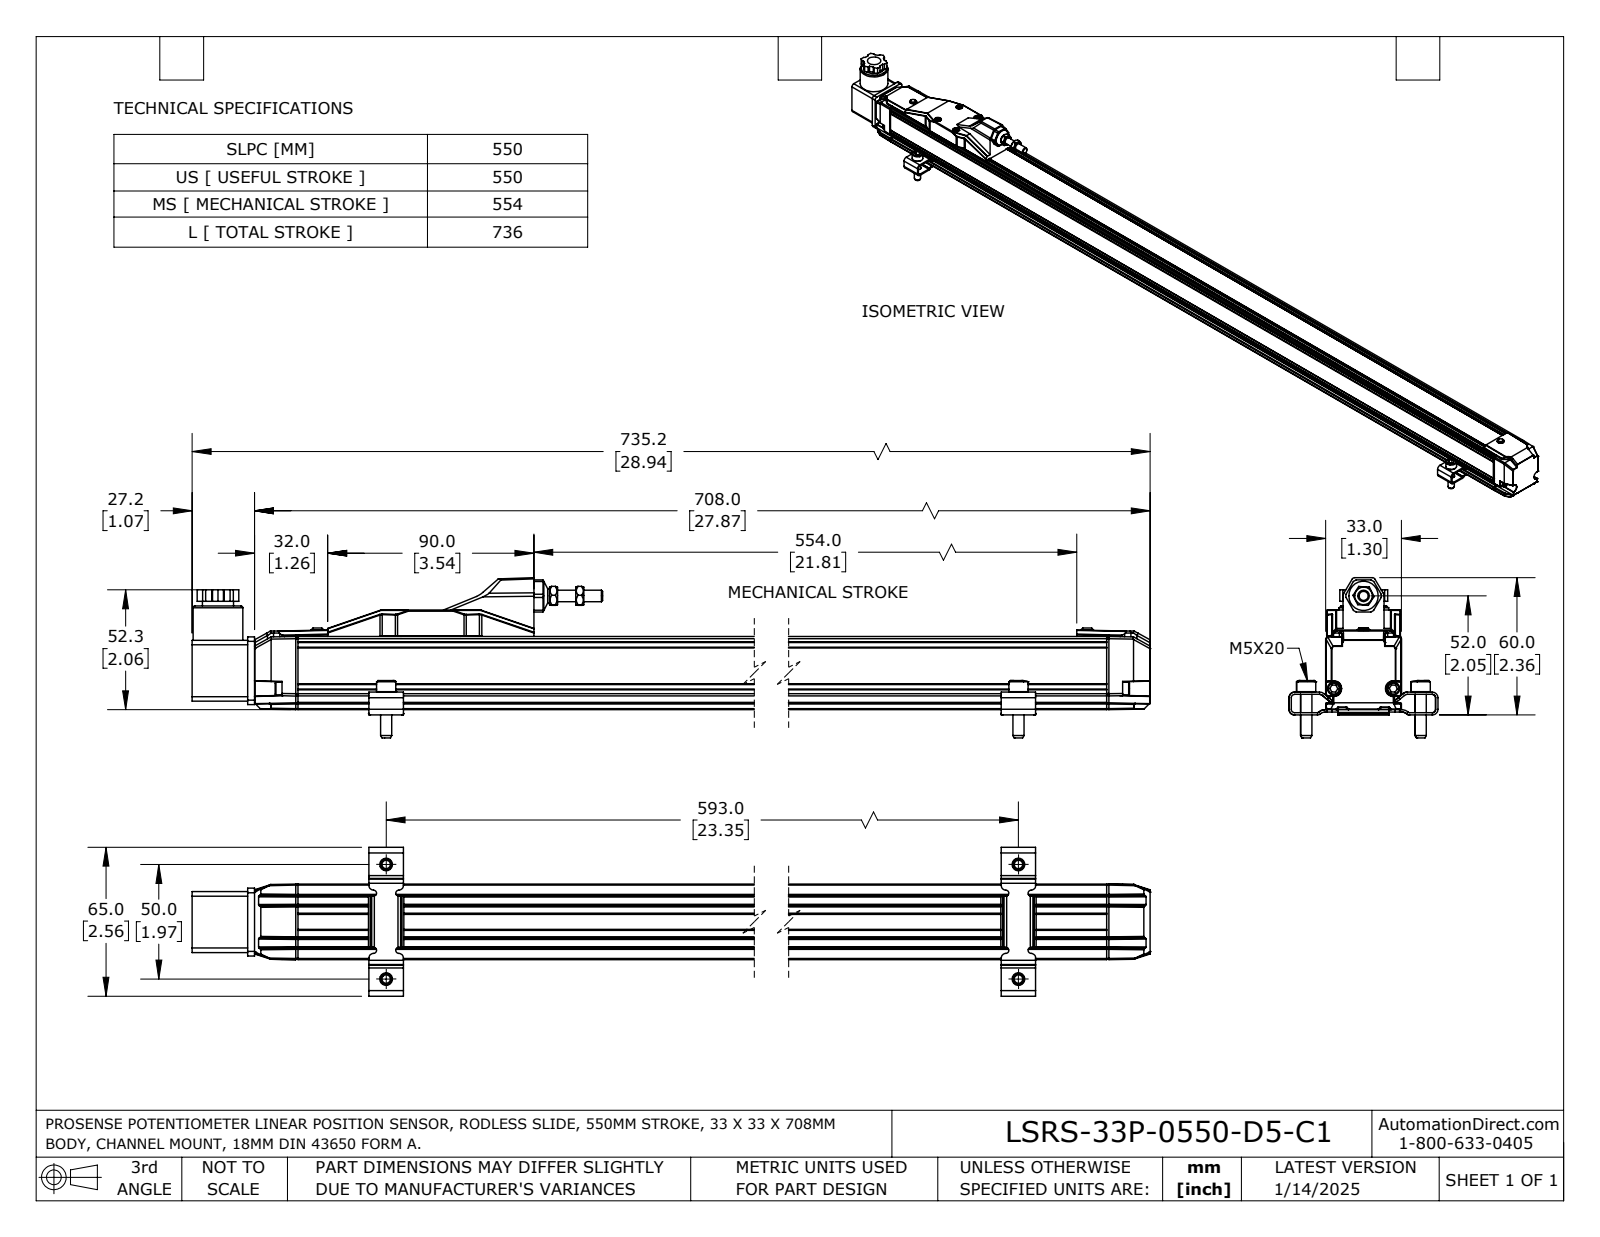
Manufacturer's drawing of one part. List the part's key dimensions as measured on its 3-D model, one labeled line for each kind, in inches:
Part name (STEP PRODUCT): LSRS-33P-0550-D5-C1
STEP written by: SolidWorks 2023 (AUTOMOTIVE_DESIGN)
Units: inches
Bodies: 28 solids, 1319 faces (814 planar, 373 cylindrical, 132 other)
Overall size (bounding box): 28.945 × 2.754 × 2.559
Volume: 43.03 in³ · Surface area: 279 in²
Round holes (diameter × count): ⌀0.106 ×6, ⌀0.185 ×4, ⌀0.217 ×4, ⌀0.13 ×2, ⌀0.11 ×1, ⌀0.157 ×1, ⌀0.197 ×1, ⌀0.209 ×1, ⌀0.232 ×1, ⌀0.236 ×1, ⌀0.276 ×1, ⌀0.394 ×1
Round bosses / shafts (diameter × count): ⌀0.331 ×4, ⌀0.193 ×4, ⌀0.181 ×4, ⌀0.113 ×3, ⌀0.22 ×2, ⌀0.217 ×2, ⌀0.118 ×2, ⌀0.098 ×2
Partial cylindrical surfaces — rounded edges, fillets, slot ends (radius × count): R0.02 ×82, R0.008 ×62, R0.079 ×44, R0.118 ×26, R0.039 ×10, R0.051 ×8, R0.059 ×8, R0.157 ×8
Main face-to-face distances: 1.299, 0.118, 1.244, 1.167, 0.237, 1.007, 0.035, 0.014, 1.285, 0.443
Hole centre spacings: 0.597, 0.787, 0.933, 1.221, 1.286, 1.673, 1.969, 22.191
